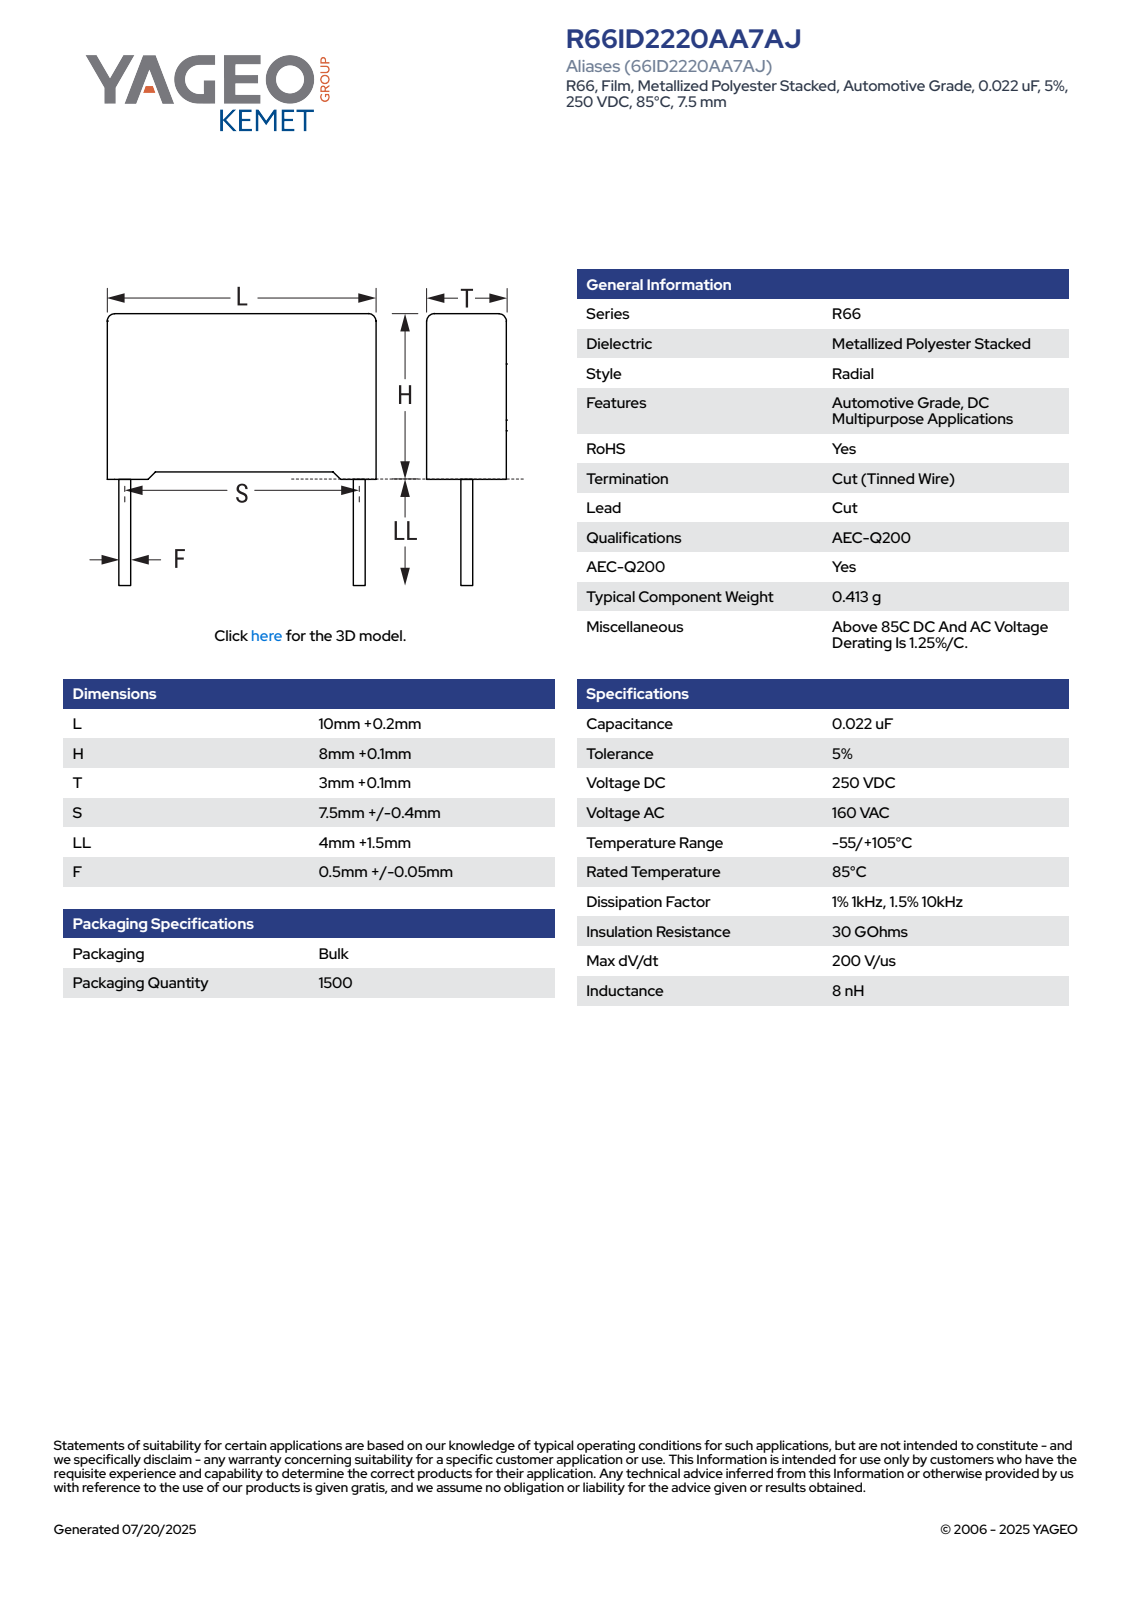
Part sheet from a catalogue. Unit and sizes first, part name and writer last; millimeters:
Units: millimetres
Overall size (bounding box): 13.6 × 10.2 × 3.1
Round bosses / shafts (diameter × count): ⌀0.55 ×2
Partial cylindrical surfaces — rounded edges, fillets, slot ends (radius × count): R0.5 ×4
Main face-to-face distances: 3.1, 10.2, 7.35, 0.34, 2.76, 2.42, 0.75, 8.1, 9.86, 0.47
Volume: 240 mm³ · Surface area: 316 mm²
Bodies: 4 solids, 85 faces (77 planar, 8 cylindrical, 0 other)
Part name (STEP PRODUCT): CFR_RB2_10X8X3_L10.2H8.1T3.1S7.5LL5.5F0.55
STEP written by: SolidWorks 2021 (AUTOMOTIVE_DESIGN)
